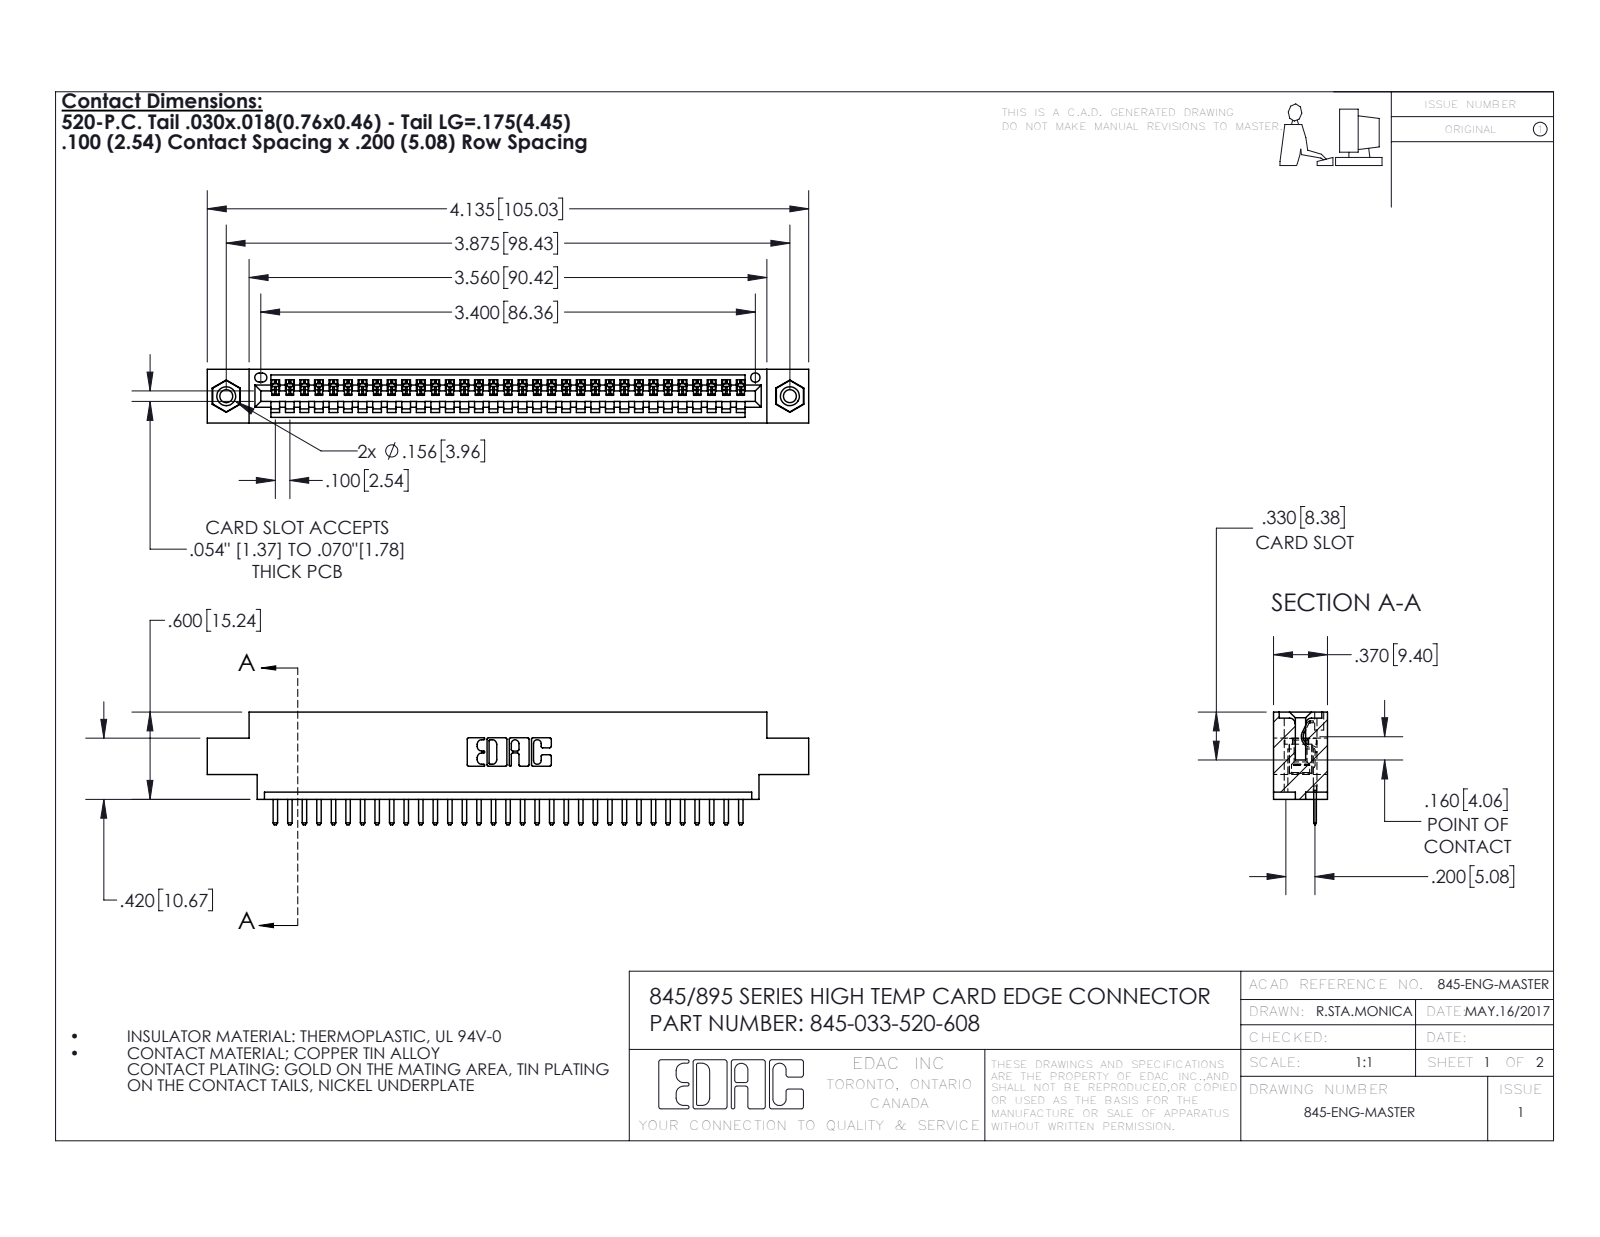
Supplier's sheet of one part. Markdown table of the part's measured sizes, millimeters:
| quantity | value |
| --- | --- |
| part name | 345-033-520-608; 345 Part_0.170 Offset - 0.156 Dia-TI; 345-292-001_345-293-120; 345-250-001_345-250-003-102 |
| STEP written by | SolidWorks 2016 (CONFIG_CONTROL_DESIGN) |
| units | millimeters |
| bodies | 36 solids, 2236 faces (1502 planar, 718 cylindrical, 16 other) |
| overall size | 105 × 19.7 × 9.4 |
| volume | 9 680 mm³ |
| surface area | 12 590 mm² |
| round holes (diameter × count) | 2.3 × 2, 3.2 × 2, 4 × 2, 1.6 × 1 |
| round bosses / shafts (diameter × count) | 3.9 × 2 |
| partial cylindrical surfaces (radius × count) | 0.3 × 68, 0.2 × 66, 0.3 × 22, 0.2 × 6, 0.8 × 6, 0.7 × 3, 0.8 × 2, 1 × 2 |
| main face-to-face distances | 1.8, 7.6, 9.4, 5.1, 2.5, 6.9, 0.6, 5.7, 1.8, 4.4 |
| hole center spacings | 6.9, 92.5, 98.4 |
